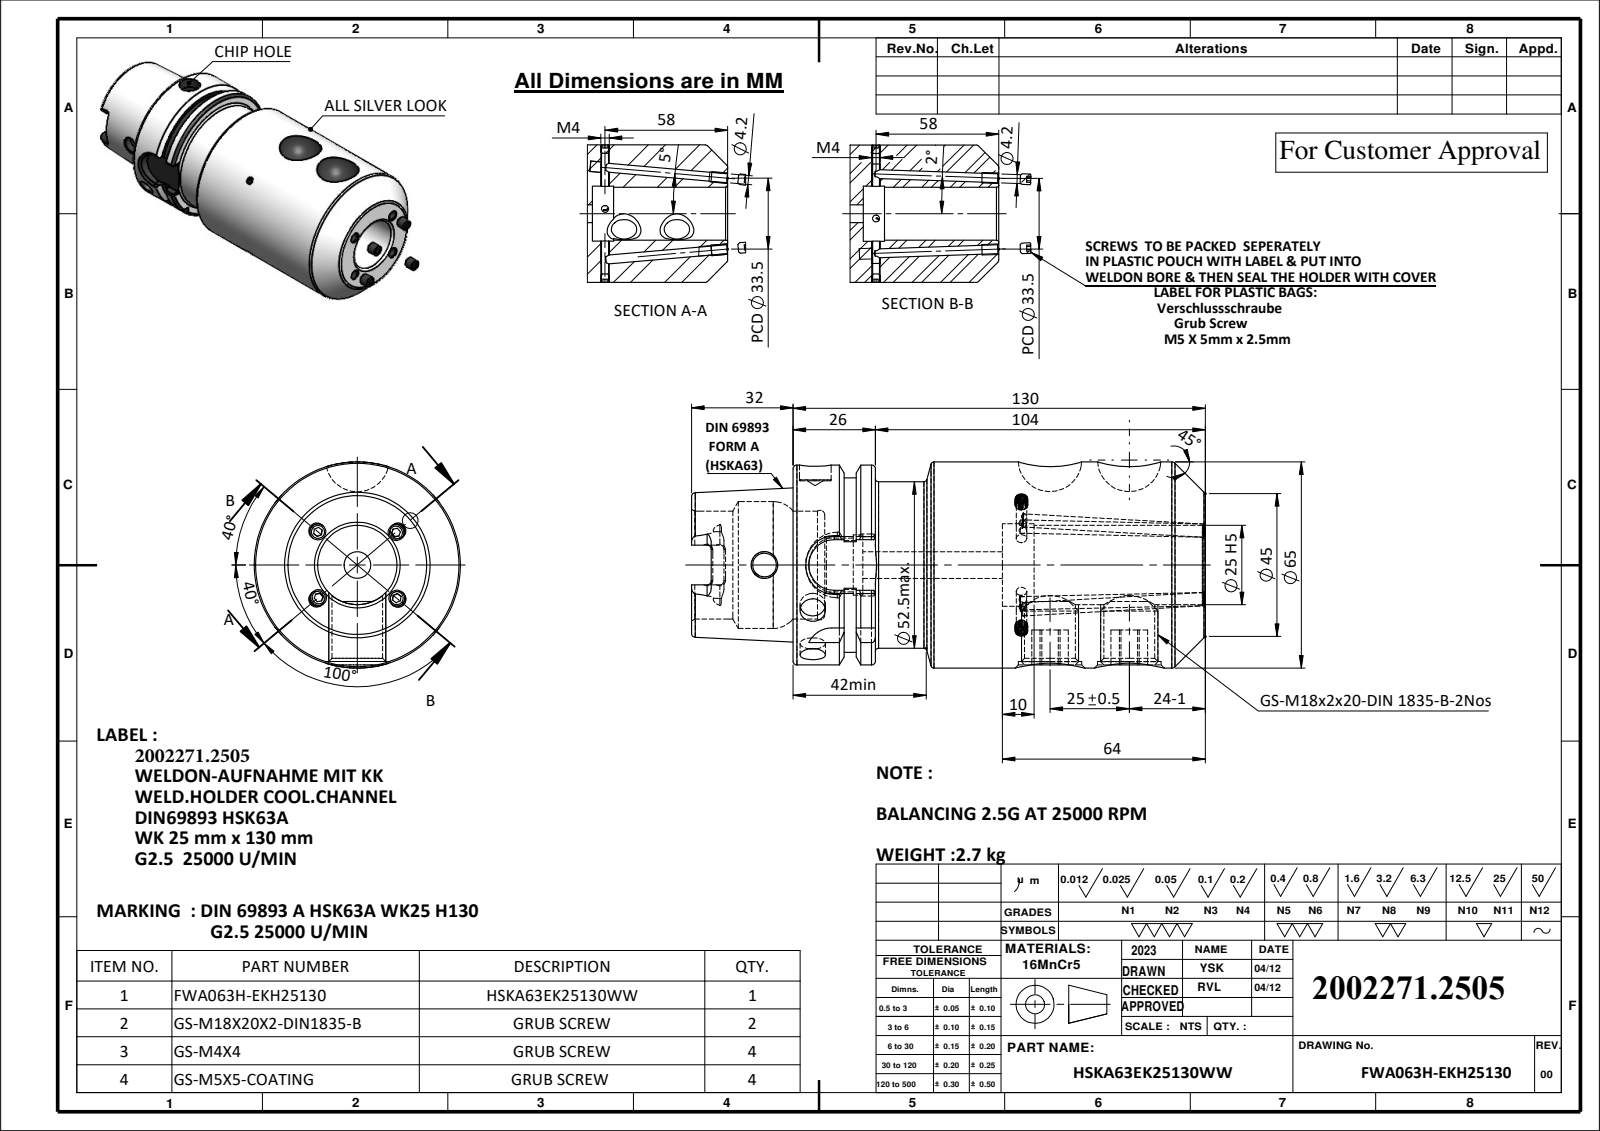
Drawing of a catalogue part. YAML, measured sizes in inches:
part_name: "HSKA63EK25130WW; FWA063H-EKH25130; GS-M5X5_DIN 913 - M5 x 5-N; GS-M18X20X2-DIN1835-B (+1 more)"
step_written_by: "SolidWorks 2023 (CONFIG_CONTROL_DESIGN)"
units: inches
bodies: {solids: 11, faces: 513, planar: 144, cylindrical: 133, other: 236}
overall_size: [6.979, 2.559, 2.559]
volume: 21.7
surface_area: 92.27
round_holes:
  - {diameter: 0.13, count: 4}
  - {diameter: 0.165, count: 4}
  - {diameter: 0.315, count: 2}
  - {diameter: 0.63, count: 2}
  - {diameter: 0.787, count: 2}
  - {diameter: 0.295, count: 1}
  - {diameter: 0.331, count: 1}
  - {diameter: 0.394, count: 1}
  - {diameter: 0.669, count: 1}
  - {diameter: 0.748, count: 1}
  - {diameter: 0.984, count: 1}
  - {diameter: 1.024, count: 1}
round_bosses_or_shafts:
  - {diameter: 0.197, count: 4}
  - {diameter: 0.157, count: 4}
  - {diameter: 0.709, count: 2}
  - {diameter: 2.559, count: 1}
  - {diameter: 2.48, count: 1}
  - {diameter: 2.165, count: 1}
  - {diameter: 2.067, count: 1}
partial_cylinders:
  - {radius: 0.051, count: 6}
  - {radius: 0.113, count: 4}
  - {radius: 0.315, count: 2}
  - {radius: 0.354, count: 1}
face_to_face_distances: [5.118, 0.394, 4.724, 2.598, 2.205, 2.52, 1.022, 0.628, 1.577, 4.096]
hole_center_spacings: [0.984, 2.913, 3.898]
